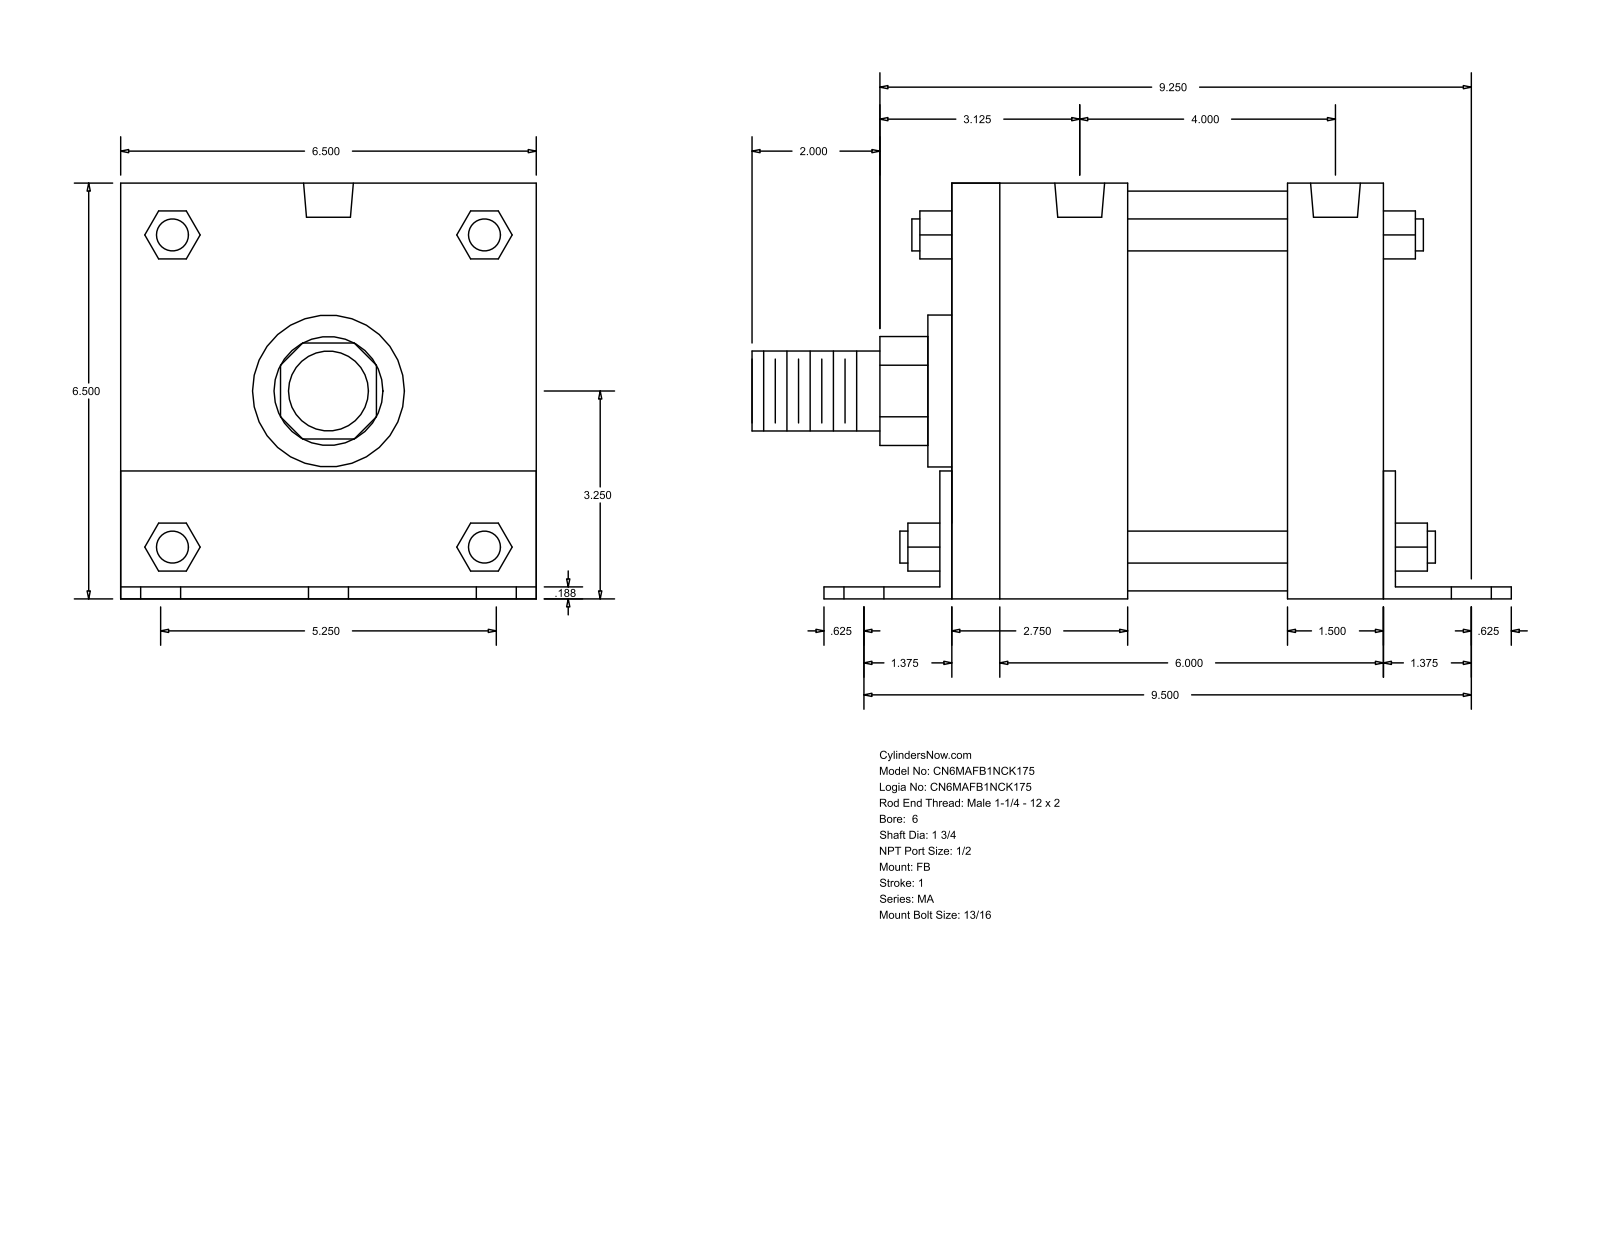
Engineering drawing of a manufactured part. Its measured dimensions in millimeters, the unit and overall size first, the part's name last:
Units: millimetres
Overall size (bounding box): 301.62 × 165.15 × 165.1
Round holes (diameter × count): ⌀20.64 ×6, ⌀17.46 ×4, ⌀19.77 ×2
Round bosses / shafts (diameter × count): ⌀12.7 ×4, ⌀158.75 ×1, ⌀60.33 ×1, ⌀44.45 ×1, ⌀31.75 ×1
Partial cylindrical surfaces — rounded edges, fillets, slot ends (radius × count): R21.63 ×1, R32.05 ×1
Main face-to-face distances: 165.1, 4.76, 171.46, 165.15, 176.22, 4.71, 160.39, 180.98, 38.1, 69.85
Hole centre spacings: 66.67, 250.34, 241.3, 85.78, 101.59, 108.6, 133.34, 169.25
Bodies: 0 solids, 140 faces (105 planar, 35 cylindrical, 0 other)
Part name (STEP PRODUCT): MA_FB__0600_1.75
STEP written by: GSSL Pune (CONFIG_CONTROL_DESIGN)
